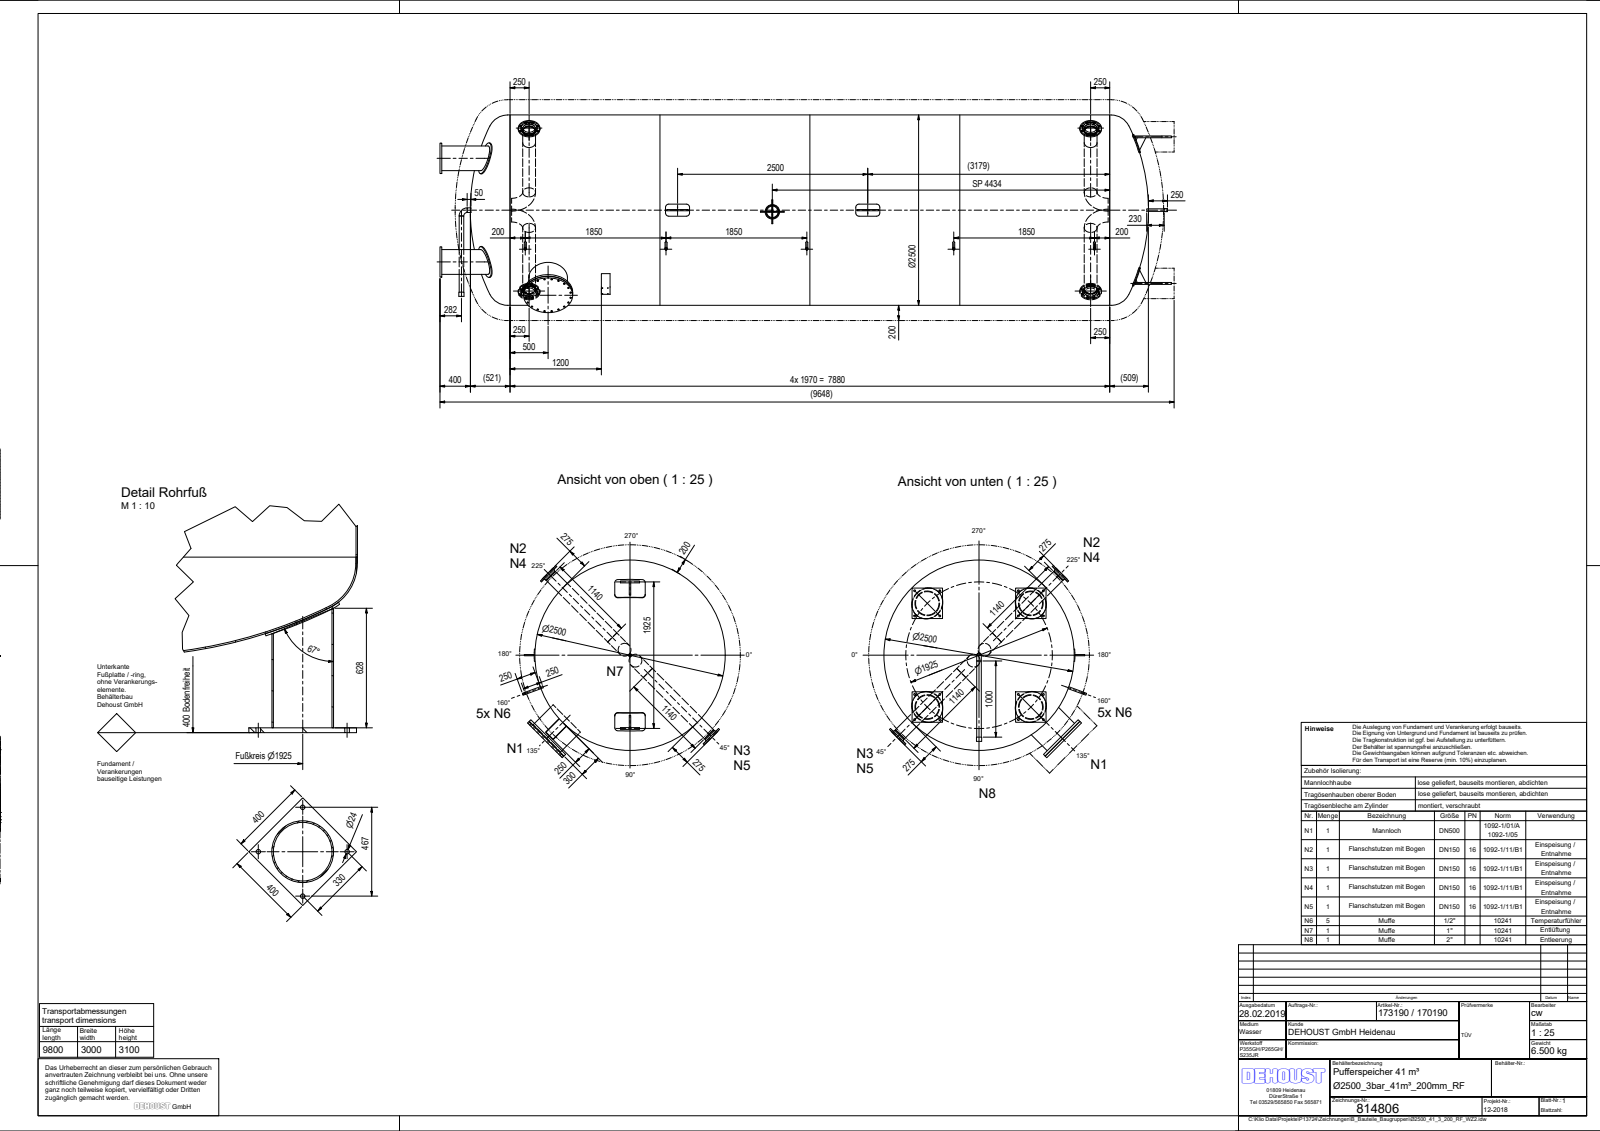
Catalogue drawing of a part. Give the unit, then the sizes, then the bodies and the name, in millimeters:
Units: millimetres
Overall size (bounding box): 9612.09 × 2664.05 × 2595.98
Round holes (diameter × count): ⌀22 ×72, ⌀24 ×16, ⌀159.3 ×8, ⌀18.63 ×5, ⌀21.7 ×5, ⌀26.9 ×5, ⌀5.8 ×4, ⌀168.3 ×4, ⌀307.9 ×4, ⌀5 ×2, ⌀52.3 ×2, ⌀508 ×2
Round bosses / shafts (diameter × count): ⌀168.3 ×8, ⌀26.9 ×5, ⌀26.4 ×5, ⌀420 ×4, ⌀323.9 ×4, ⌀285 ×4, ⌀212 ×4, ⌀645 ×2
Partial cylindrical surfaces — rounded edges, fillets, slot ends (radius × count): R42 ×16, R6 ×8, R5 ×2, R10 ×2, R36 ×2, R72 ×2, R125 ×1, R1259 ×1
Main face-to-face distances: 25, 600, 4628.97, 5093.97, 4603.97, 5068.97, 465, 27.99, 650, 1250
Hole centre spacings: 300, 120, 120.01, 93.86, 185.41, 352.67, 7380, 485.41
Volume: 771 200 000 mm³ · Surface area: 168 900 000 mm²
Bodies: 58 solids, 453 faces (178 planar, 225 cylindrical, 50 other)
Part name (STEP PRODUCT): Ø2500_41_3_200_RF_WZ2; Klöpper_Gew_Ø2500_5,5; Klöpper_Gew_Ø2500_8,3; Zyl_Ø2500_7x7880_2019 (+8 more)
STEP written by: Autodesk Inventor 2019 (AUTOMOTIVE_DESIGN)
